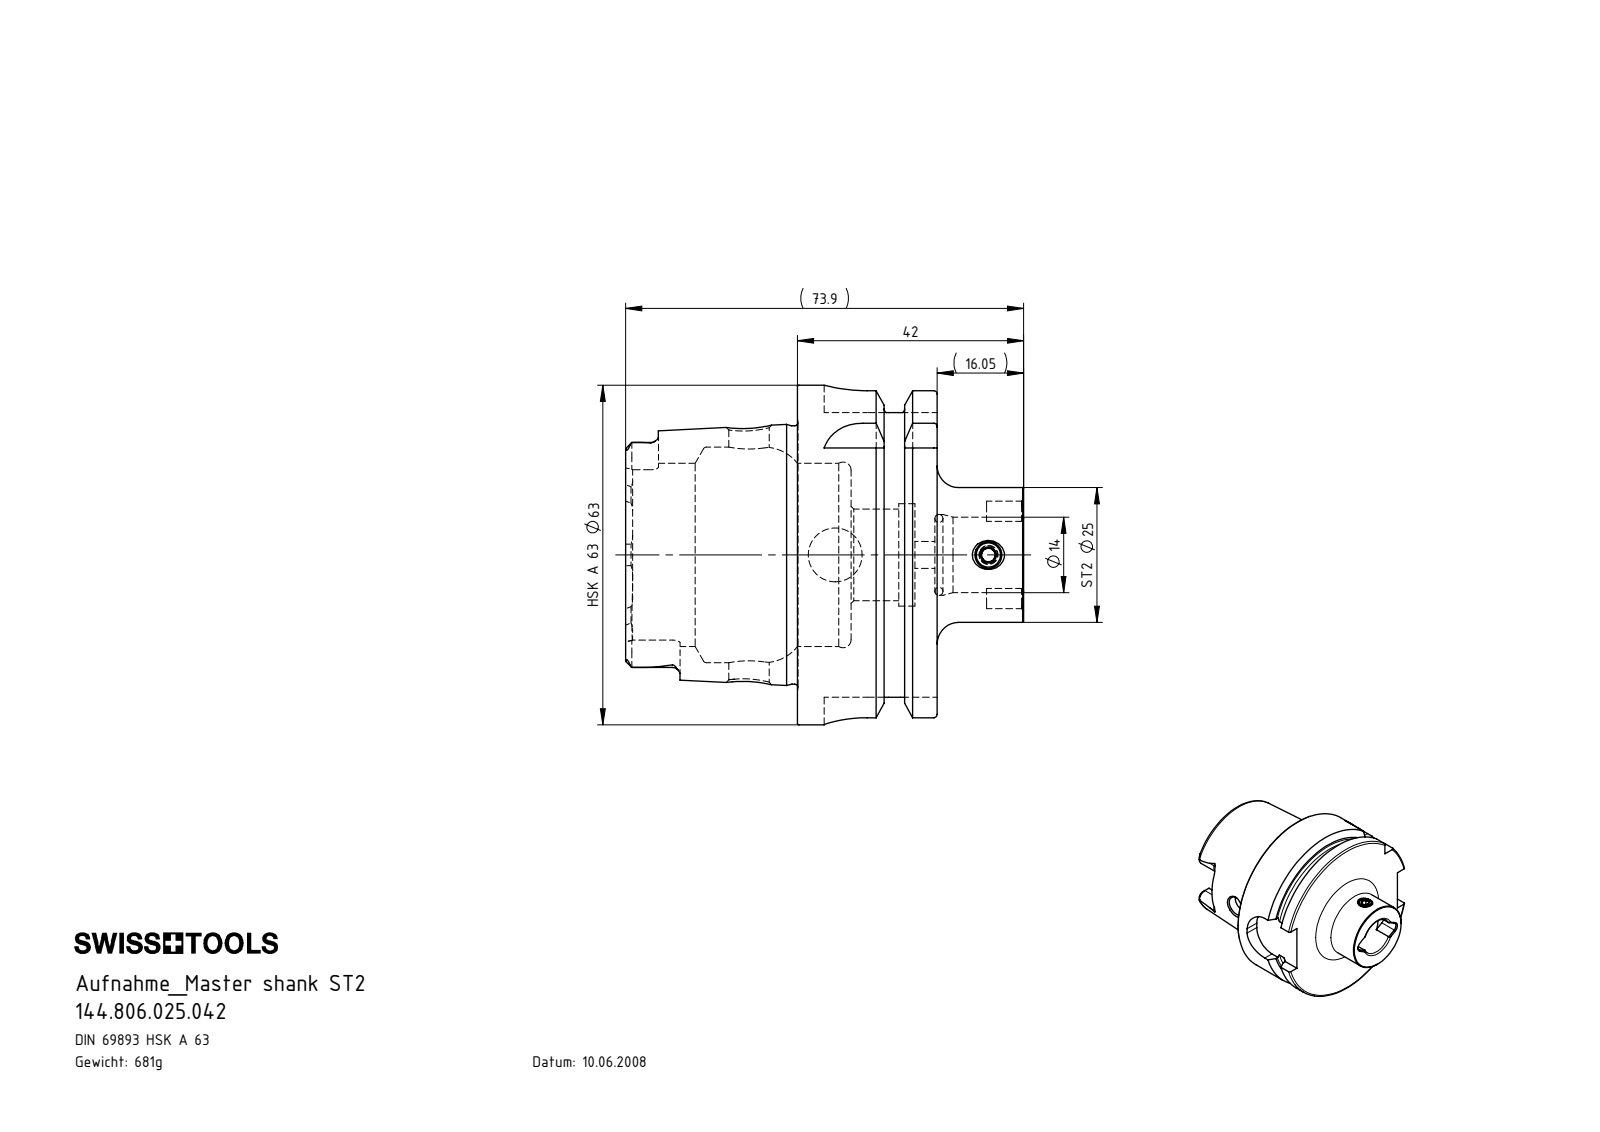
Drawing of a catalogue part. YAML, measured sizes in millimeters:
part_name: "144.806.025.042; ST2-ER1.001.006_A; DIN 3771 - 12x1.5; HA6-ST2.K01.042_B_Fertigbearbeitung"
step_written_by: "SolidWorks 2017 (CONFIG_CONTROL_DESIGN)"
units: millimeters
bodies: {solids: 3, faces: 227, planar: 69, cylindrical: 58, other: 100}
overall_size: [73.9, 63, 63]
volume: 86869
surface_area: 24537
round_holes:
  - {diameter: 2.5, count: 1}
  - {diameter: 4.5, count: 1}
  - {diameter: 5, count: 1}
  - {diameter: 7.5, count: 1}
  - {diameter: 10, count: 1}
  - {diameter: 14, count: 1}
  - {diameter: 15, count: 1}
  - {diameter: 17, count: 1}
  - {diameter: 19, count: 1}
  - {diameter: 34, count: 1}
  - {diameter: 40, count: 1}
round_bosses_or_shafts:
  - {diameter: 63, count: 1}
  - {diameter: 54.95, count: 1}
  - {diameter: 47.94, count: 1}
  - {diameter: 25, count: 1}
  - {diameter: 5, count: 1}
partial_cylinders:
  - {radius: 1.4, count: 6}
  - {radius: 2.88, count: 4}
  - {radius: 8, count: 4}
  - {radius: 1.8, count: 2}
face_to_face_distances: [25.95, 16, 9.95, 31.9, 41.85, 57.85, 21.8, 52.8, 11.85, 73.9]
hole_center_spacings: [28.45]
